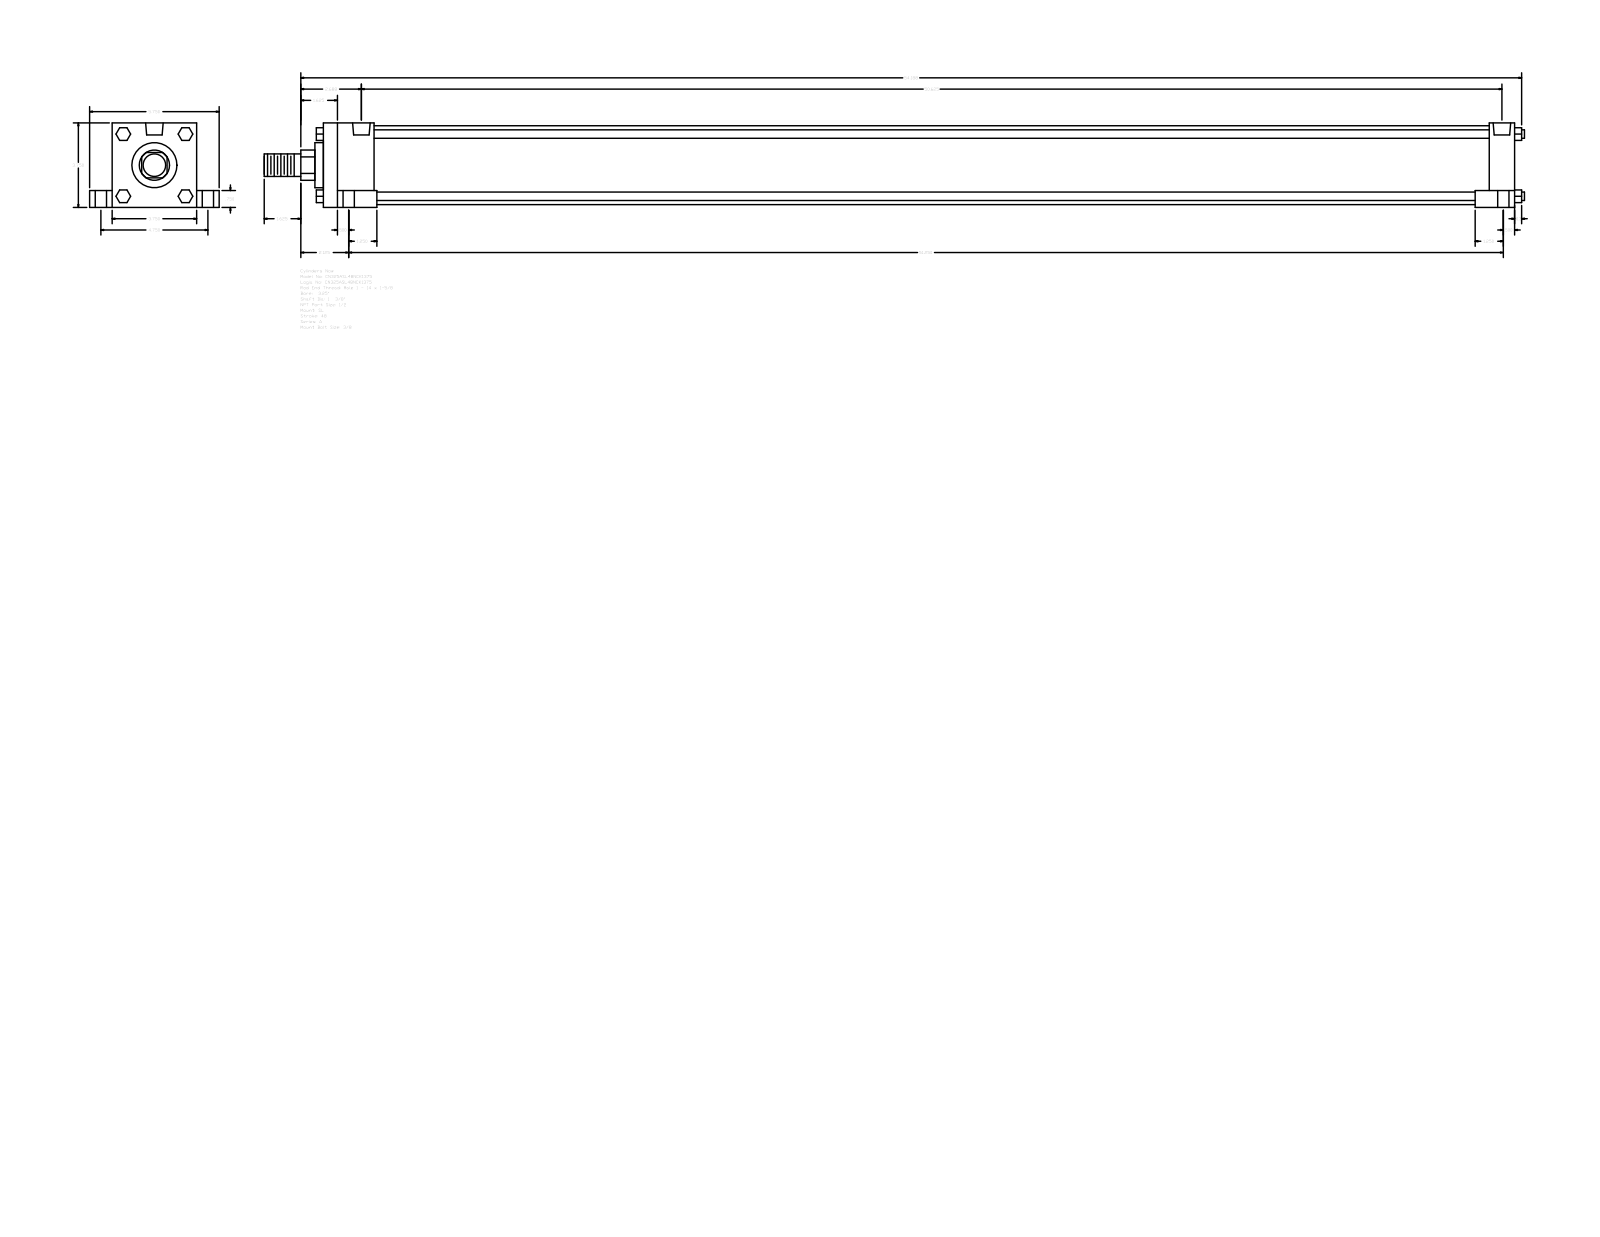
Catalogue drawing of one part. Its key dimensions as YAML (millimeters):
part_name: "A_SL__0325_1.375"
step_written_by: "GSSL Pune (CONFIG_CONTROL_DESIGN)"
units: millimeters
bodies: {solids: 0, faces: 150, planar: 114, cylindrical: 36, other: 0}
overall_size: [1420.81, 146.05, 95.25]
round_holes:
  - {diameter: 8.73, count: 4}
  - {diameter: 12.7, count: 4}
  - {diameter: 19.05, count: 4}
  - {diameter: 19.77, count: 2}
round_bosses_or_shafts:
  - {diameter: 9.53, count: 4}
  - {diameter: 88.9, count: 1}
  - {diameter: 50.8, count: 1}
  - {diameter: 34.92, count: 1}
  - {diameter: 25.4, count: 1}
partial_cylinders:
  - {radius: 17.06, count: 1}
face_to_face_distances: [95.24, 1343.02, 25.41, 120.65, 19.05, 76.19, 57.15, 28.57, 1314.45, 1257.3]
hole_center_spacings: [3.18, 60.35, 60.52, 62, 62.81, 120.66, 1279.52, 1282.7]
